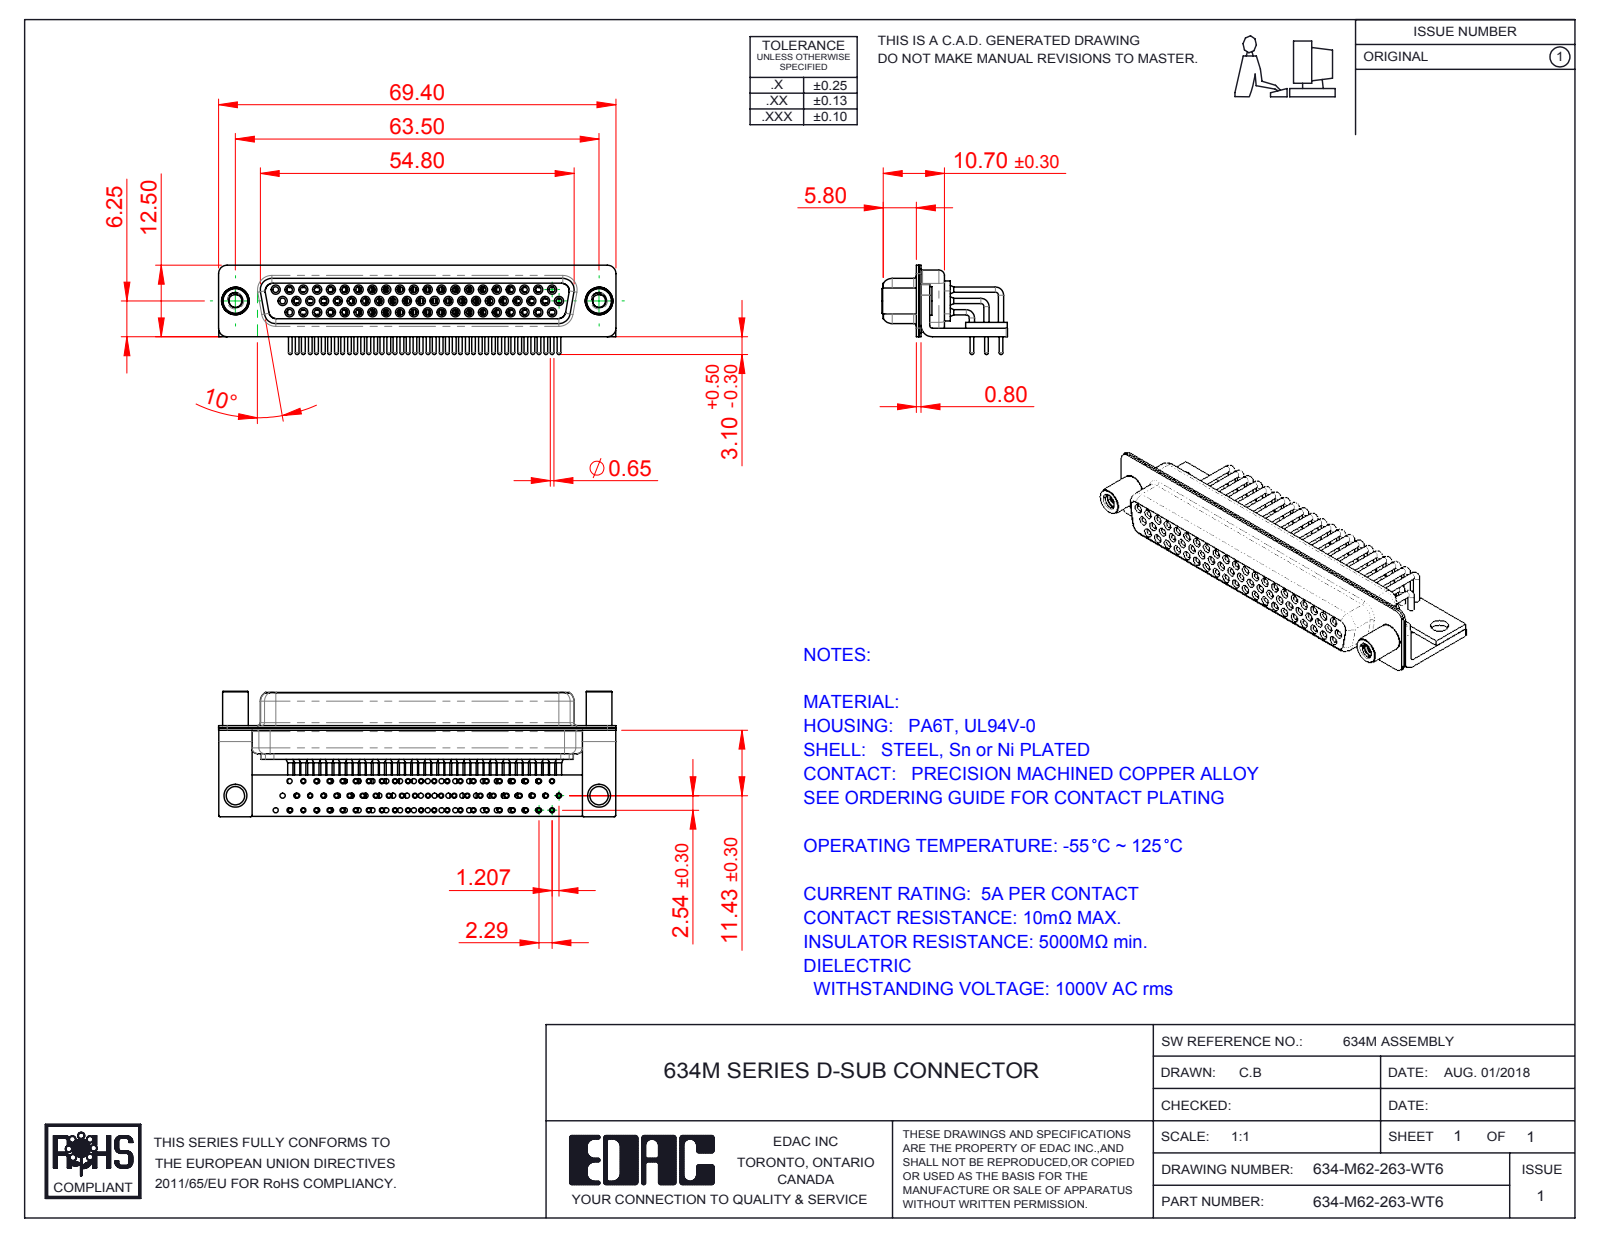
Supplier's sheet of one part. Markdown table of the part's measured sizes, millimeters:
| quantity | value |
| --- | --- |
| part name | 634M Shell Rear_62 Contacts; 634-M62-263-WT6; 634M Housing_62 Contacts; 634M Stabilizer Board_62 Contacts (+6 more) |
| STEP written by | SolidWorks 2016 (CONFIG_CONTROL_DESIGN) |
| units | millimeters |
| bodies | 70 solids, 3789 faces (1025 planar, 1751 cylindrical, 1013 other) |
| overall size | 69.4 × 21.9 × 15.6 |
| volume | 6 258 mm³ |
| surface area | 20 041 mm² |
| round holes (diameter × count) | 0.9 × 62, 1 × 62, 1.1 × 62, 1.7 × 62, 1.8 × 62, 2 × 62, 2.26 × 2, 3.2 × 2, 4 × 2, 4.8 × 2 |
| round bosses / shafts (diameter × count) | 0.9 × 118, 1.6 × 62, 1.5 × 62, 0.65 × 62, 2 × 56, 5 × 2, 4.9 × 2, 4.5 × 2 |
| partial cylindrical surfaces (radius × count) | 0.25 × 16, 1.5 × 16, 2 × 13, 1.35 × 8, 1.6 × 8, 0.5 × 5, 0.6 × 4, 0.65 × 4 |
| main face-to-face distances | 0.4, 2.3, 1.9, 1, 8.5, 1.45, 8.95, 0.85, 0.8, 6.2 |
| hole center spacings | 7.24, 2.41, 9.65, 4.83, 14.48, 16.89, 2.81, 2.32 |
